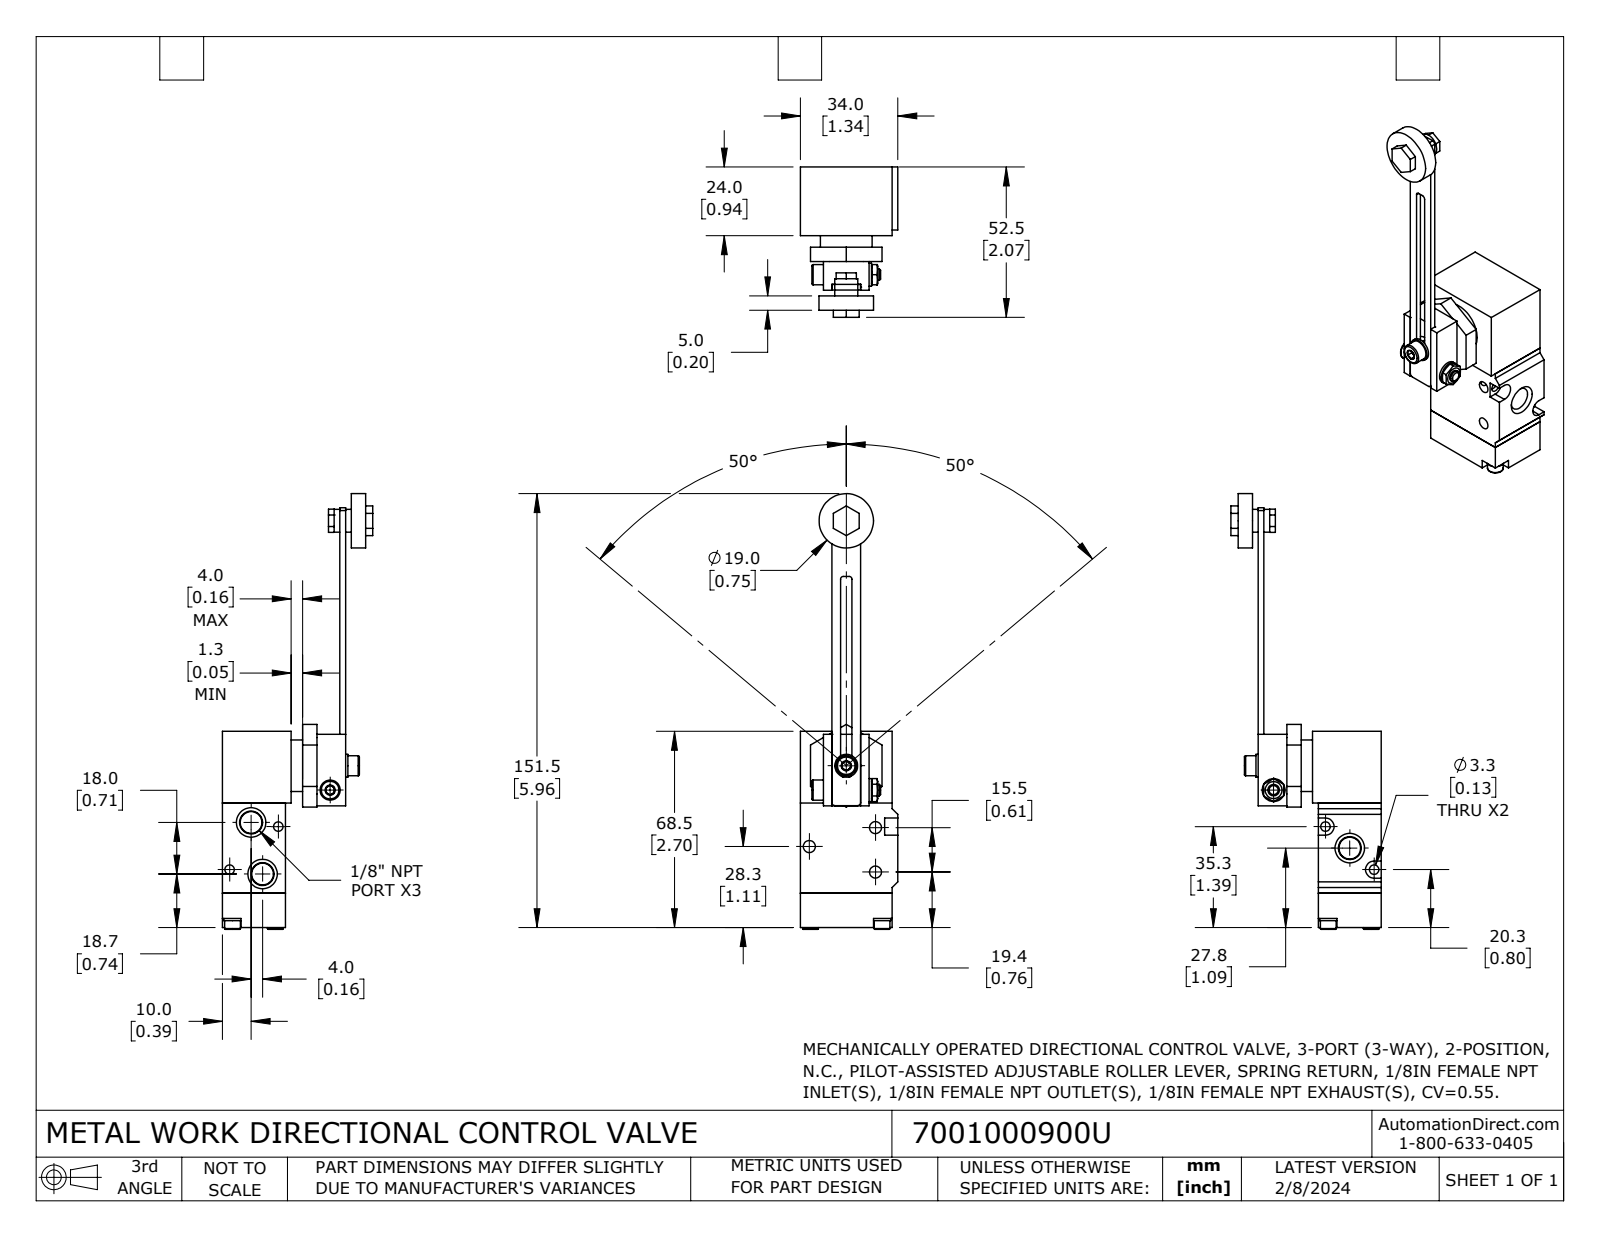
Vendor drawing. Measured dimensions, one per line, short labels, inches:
name: 7001000900U
written by: SolidWorks 2023 (CONFIG_CONTROL_DESIGN)
unit: in
bodies: 14 solids, 326 faces (173 planar, 77 cylindrical, 76 other)
size: 5.988 × 2.067 × 1.339
volume: 3.599 in³; area: 34.39 in²
holes: 4× ⌀0.165, 3× ⌀0.157, 2× ⌀0.118, 2× ⌀0.13, 1× ⌀0.128, 1× ⌀0.315
bosses: 2× ⌀0.315, 2× ⌀0.276, 2× ⌀0.236, 2× ⌀0.217, 1× ⌀0.748, 1× ⌀0.709
rounds: 8× R0.039, 2× R0.118, 1× R0.004
face distances: 0.079, 1.24, 0.315, 0.866, 0.433, 0.945, 0.984, 0.826, 0.748, 0.512
hole spacings: 0.61, 0.872, 0.893, 0.941, 0.946, 0.975, 1.148, 1.221
